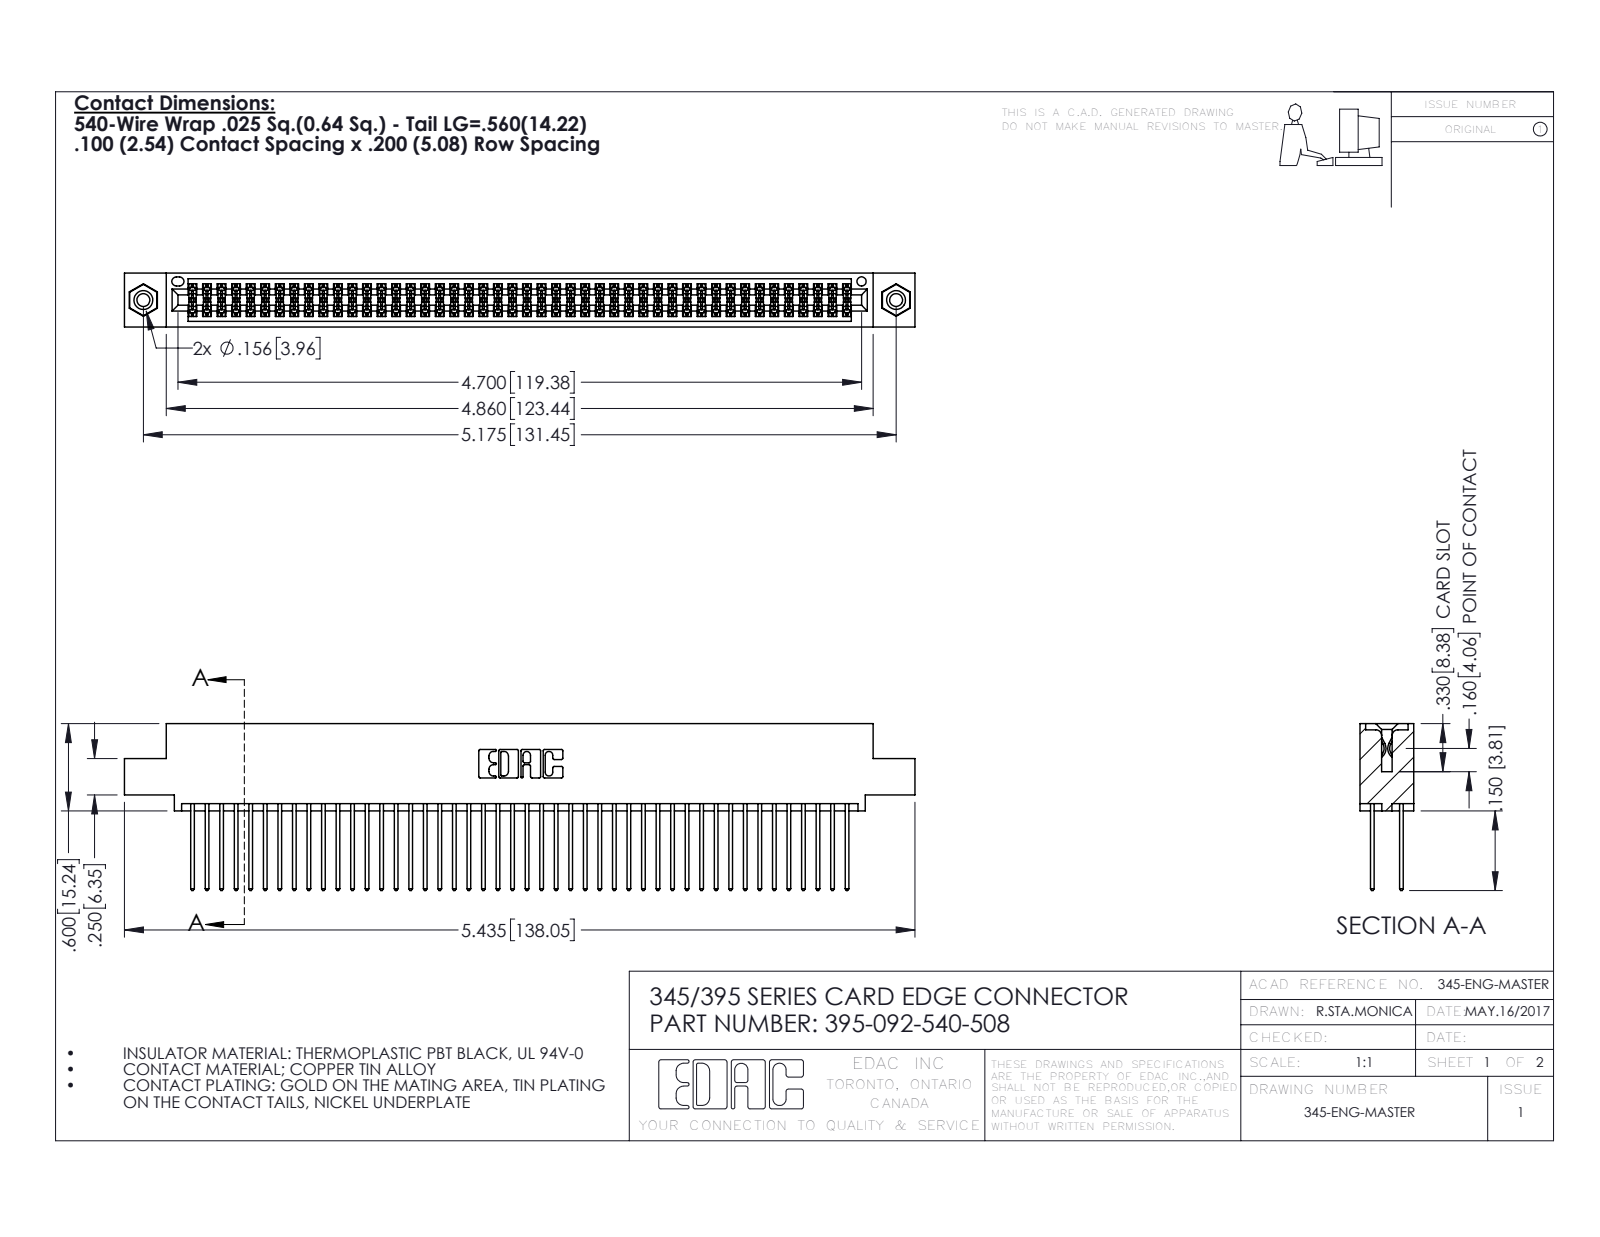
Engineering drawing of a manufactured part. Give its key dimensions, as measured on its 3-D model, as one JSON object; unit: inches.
{"part_name": "345-292-001_345-293-140; 395-092-540-508; 345 Part_0.110 Offset - 0.156 Dia-TI; 345-250-001_345-250-003-102", "step_written_by": "SolidWorks 2016 (CONFIG_CONTROL_DESIGN)", "units": "inches", "bodies": {"solids": 95, "faces": 4790, "planar": 3152, "cylindrical": 1622, "other": 16}, "overall_size": [5.435, 1.147, 0.37], "volume_in3": 0.837, "surface_area_in2": 34.22, "round_holes": [[0.089, 2], [0.125, 2], [0.156, 2], [0.064, 1]], "round_bosses_or_shafts": [[0.155, 2]], "partial_cylinders_radius": [[0.006, 138], [0.01, 92], [0.01, 22], [0.007, 6], [0.031, 6], [0.026, 3], [0.014, 2], [0.019, 2]], "face_to_face_distances": [0.072, 0.298, 0.2, 0.098, 0.272, 0.025, 0.37, 0.225, 0.175, 0.149], "hole_center_spacings": [0.27, 4.939, 5.175]}
